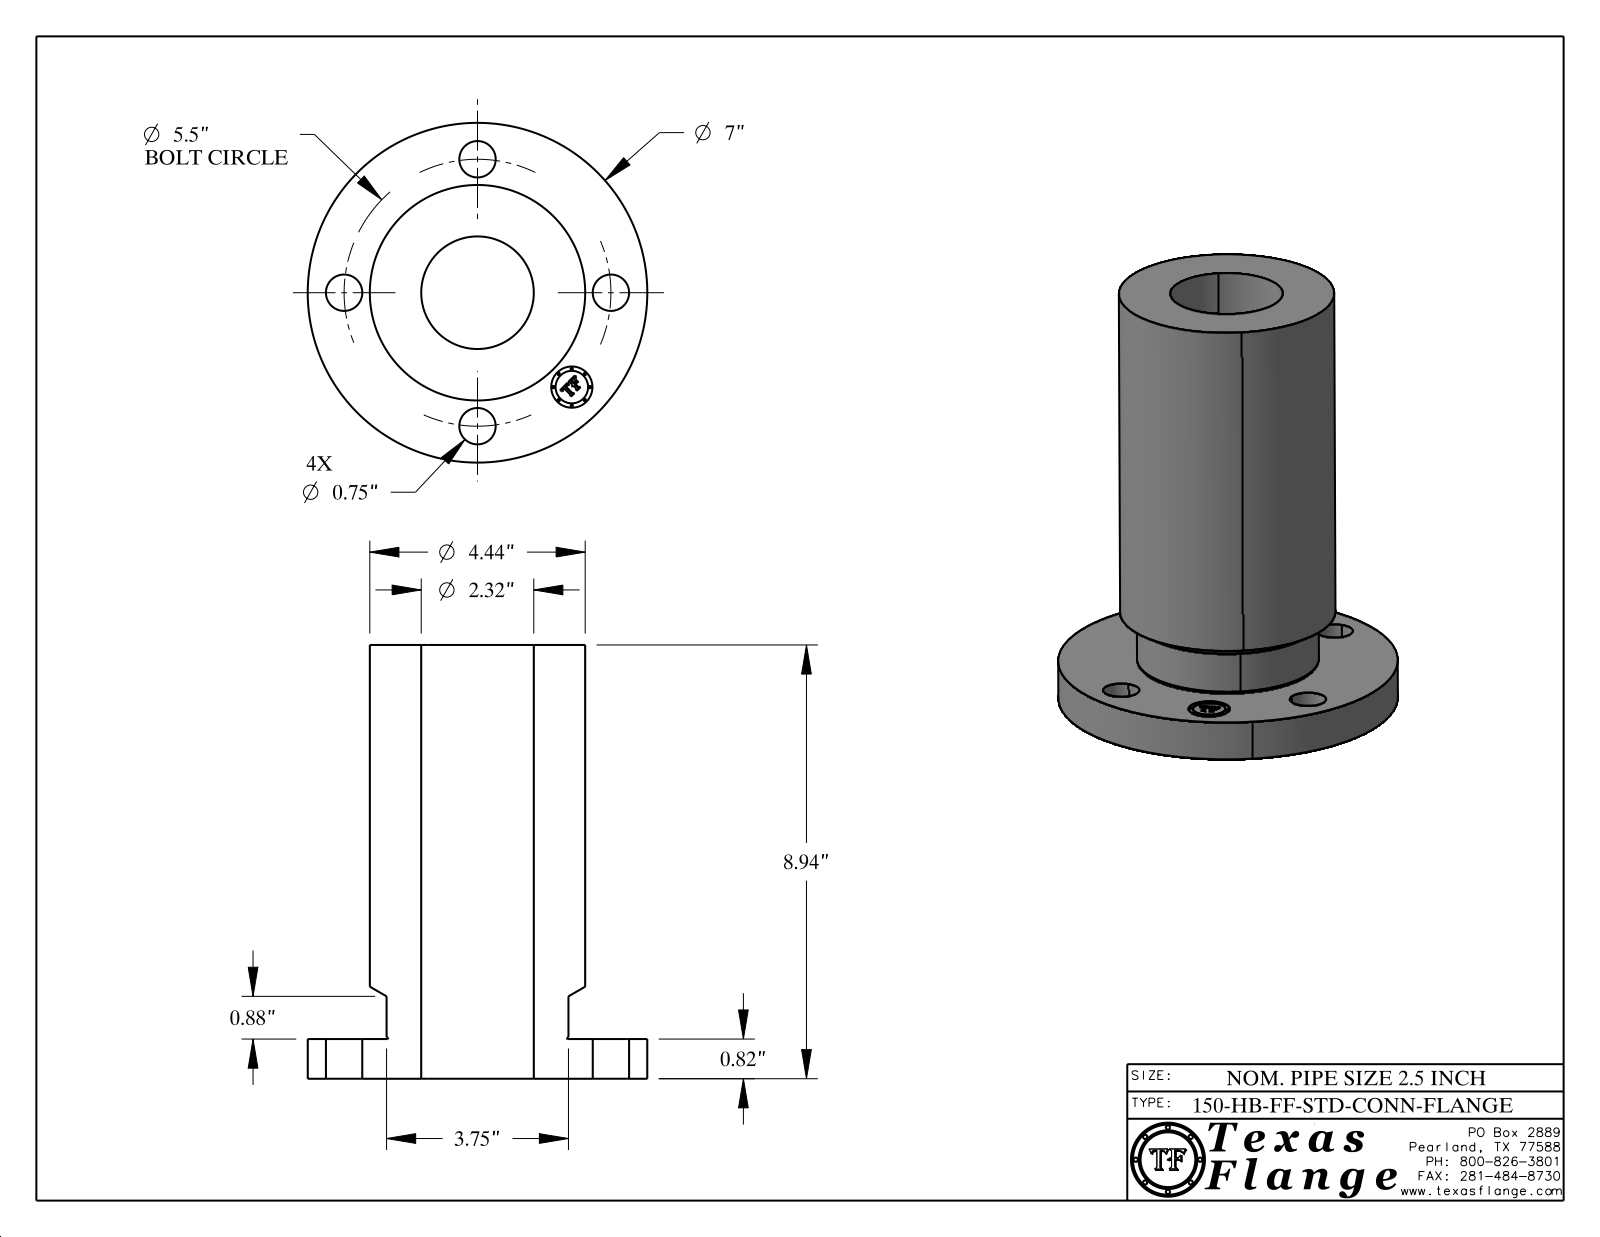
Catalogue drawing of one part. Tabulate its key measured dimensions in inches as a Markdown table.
| quantity | value |
| --- | --- |
| part name | 2.5-150-HB-FF-STD-CONN-FLANGE |
| STEP written by | CATIA V5 STEP AP214 (AUTOMOTIVE_DESIGN) |
| units | inches |
| bodies | 1 solid, 410 faces (368 planar, 36 cylindrical, 6 other) |
| overall size | 8.938 × 7 × 7 |
| volume | 113.6 in³ |
| surface area | 274.5 in² |
| round holes (diameter × count) | 0.75 × 4, 0.85 × 1, 2.32 × 1 |
| round bosses / shafts (diameter × count) | 0.051 × 8, 7 × 1, 4.44 × 1, 3.75 × 1, 0.67 × 1 |
| main face-to-face distances | 0.817, 8.937, 8.12, 0.813, 8.125, 0.254, 0.248, 0.016, 0.046, 0.165 |
| hole center spacings | 2.75, 3.889, 2.105, 5.081, 5.5 |
